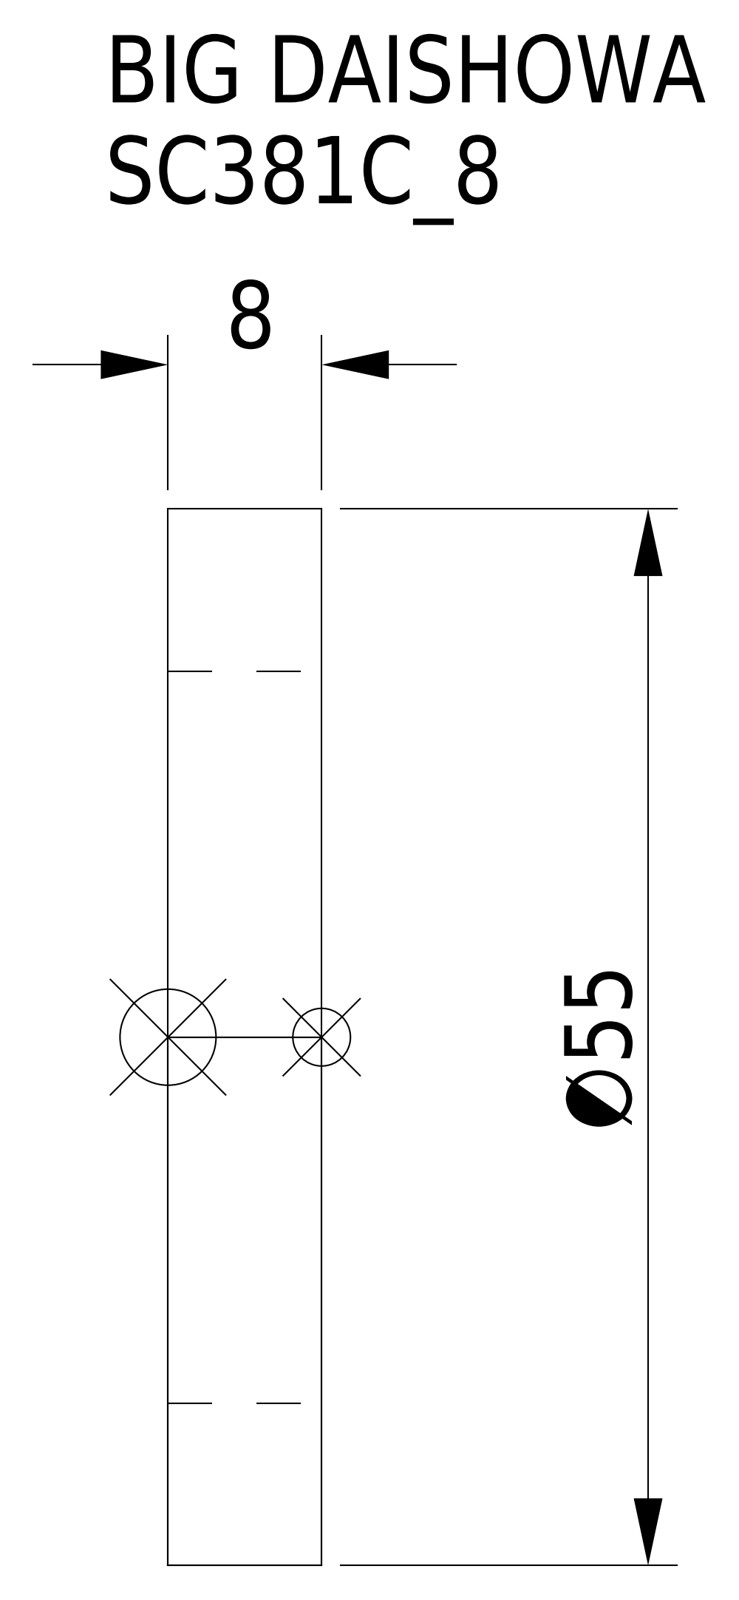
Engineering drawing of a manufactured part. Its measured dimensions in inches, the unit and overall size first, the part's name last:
Units: inches
Overall size (bounding box): 2.165 × 2.165 × 0.315
Round holes (diameter × count): ⌀1.5 ×1
Round bosses / shafts (diameter × count): ⌀2.165 ×1
Main face-to-face distances: 0.315, 0.386
Volume: 0.582 in³ · Surface area: 7.442 in²
Bodies: 1 solid, 8 faces (5 planar, 3 cylindrical, 0 other)
Part name (STEP PRODUCT): SC381C_8
STEP written by: CREO PARAMETRIC BY PTC INC, 2016380 (AUTOMOTIVE_DESIGN)
